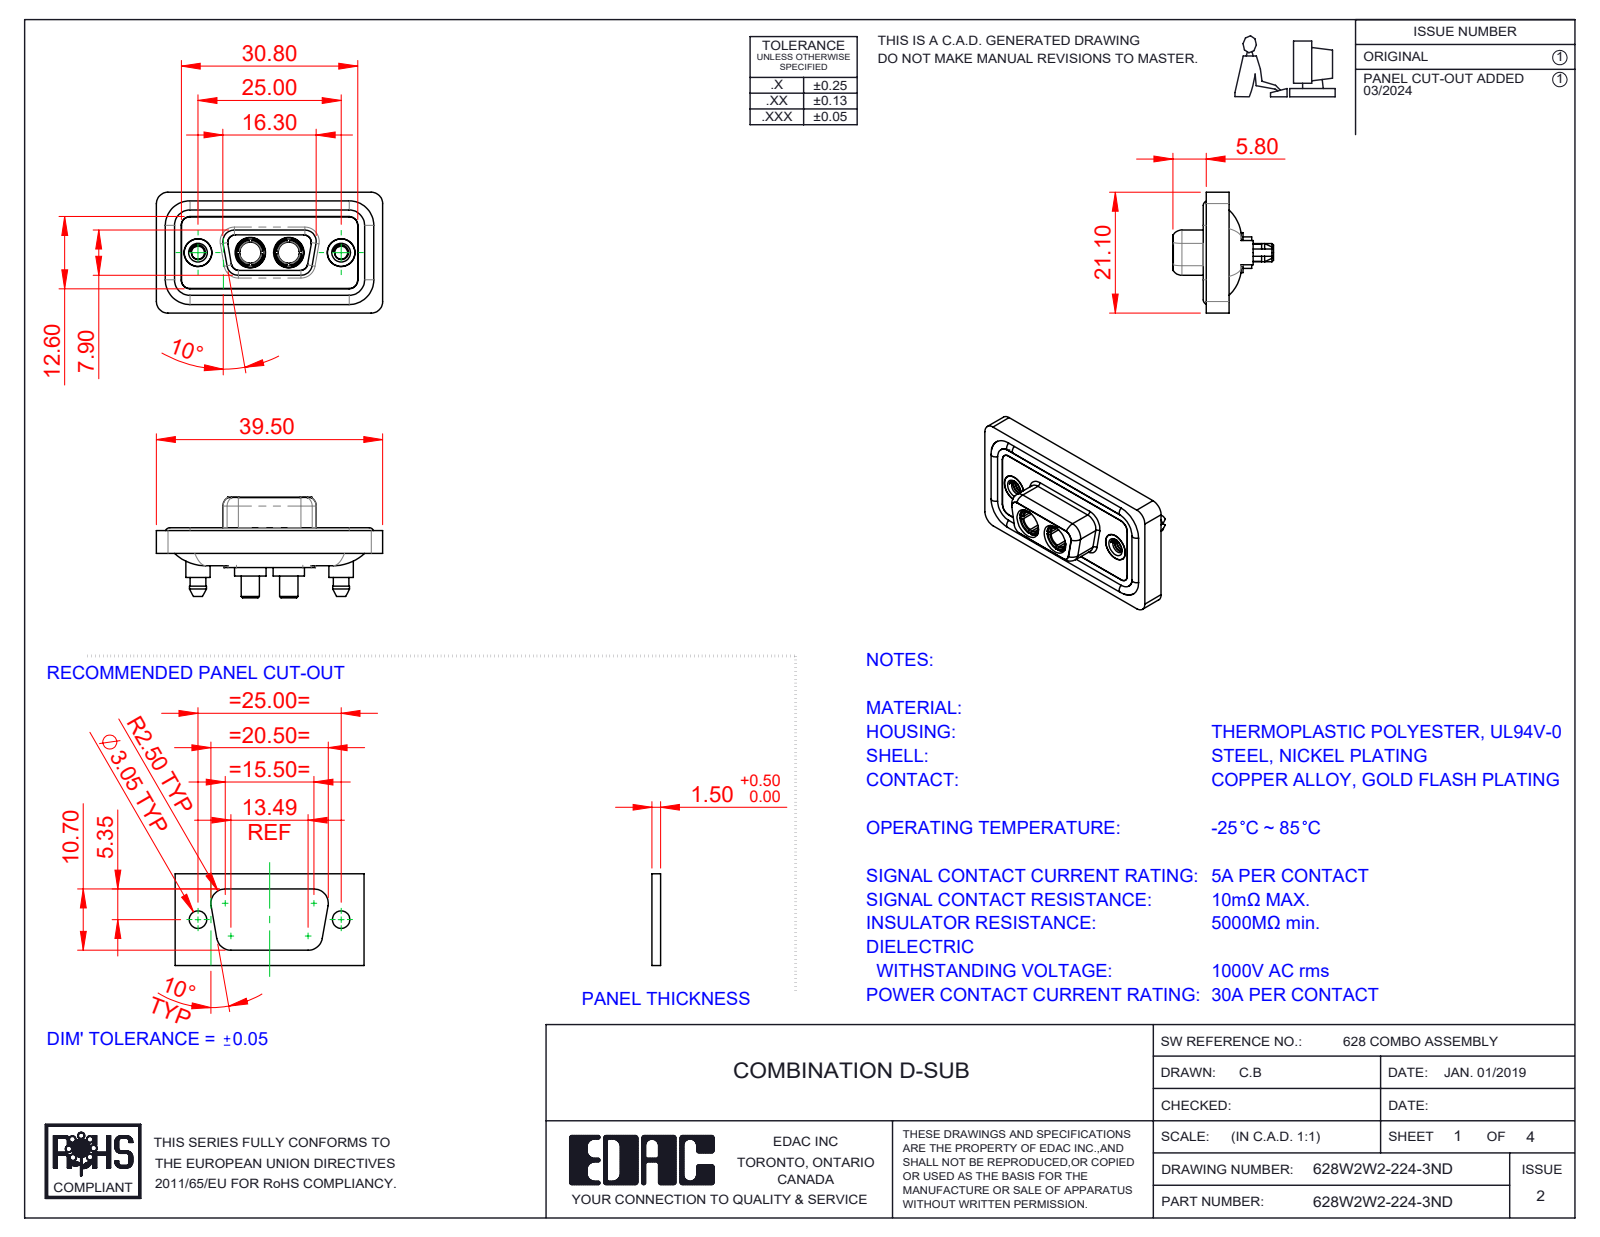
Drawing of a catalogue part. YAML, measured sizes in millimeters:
part_name: "628W2W2-224-3ND; 628Combo Housing_2W2; 628Combo Threaded Boardlock_D; 628Combo Waterproof Housing_09 Contacts (+3 more)"
step_written_by: "SolidWorks 2023 (CONFIG_CONTROL_DESIGN)"
units: millimeters
bodies: {solids: 11, faces: 600, planar: 179, cylindrical: 282, other: 139}
overall_size: [39.5, 21.1, 17.55]
volume: 4862
surface_area: 7984
round_holes:
  - {diameter: 4.85, count: 4}
  - {diameter: 2.26, count: 2}
  - {diameter: 3.7, count: 2}
  - {diameter: 4, count: 2}
  - {diameter: 4.05, count: 2}
  - {diameter: 5, count: 2}
  - {diameter: 5.3, count: 2}
round_bosses_or_shafts:
  - {diameter: 1.6, count: 4}
  - {diameter: 5.5, count: 2}
  - {diameter: 5.4, count: 2}
  - {diameter: 5.2, count: 2}
  - {diameter: 4.96, count: 2}
  - {diameter: 4.95, count: 2}
  - {diameter: 4.8, count: 2}
  - {diameter: 4.75, count: 2}
partial_cylinders:
  - {radius: 1.5, count: 24}
  - {radius: 2, count: 18}
  - {radius: 1.6, count: 10}
  - {radius: 1.35, count: 8}
  - {radius: 0.25, count: 4}
  - {radius: 0.5, count: 4}
  - {radius: 0.6, count: 4}
  - {radius: 0.65, count: 4}
face_to_face_distances: [0.4, 1.8, 1.1, 2.9, 1.6, 0.5, 5.65, 7.45, 1.5, 4]
hole_center_spacings: [9.14, 15.86, 6.72, 25]
